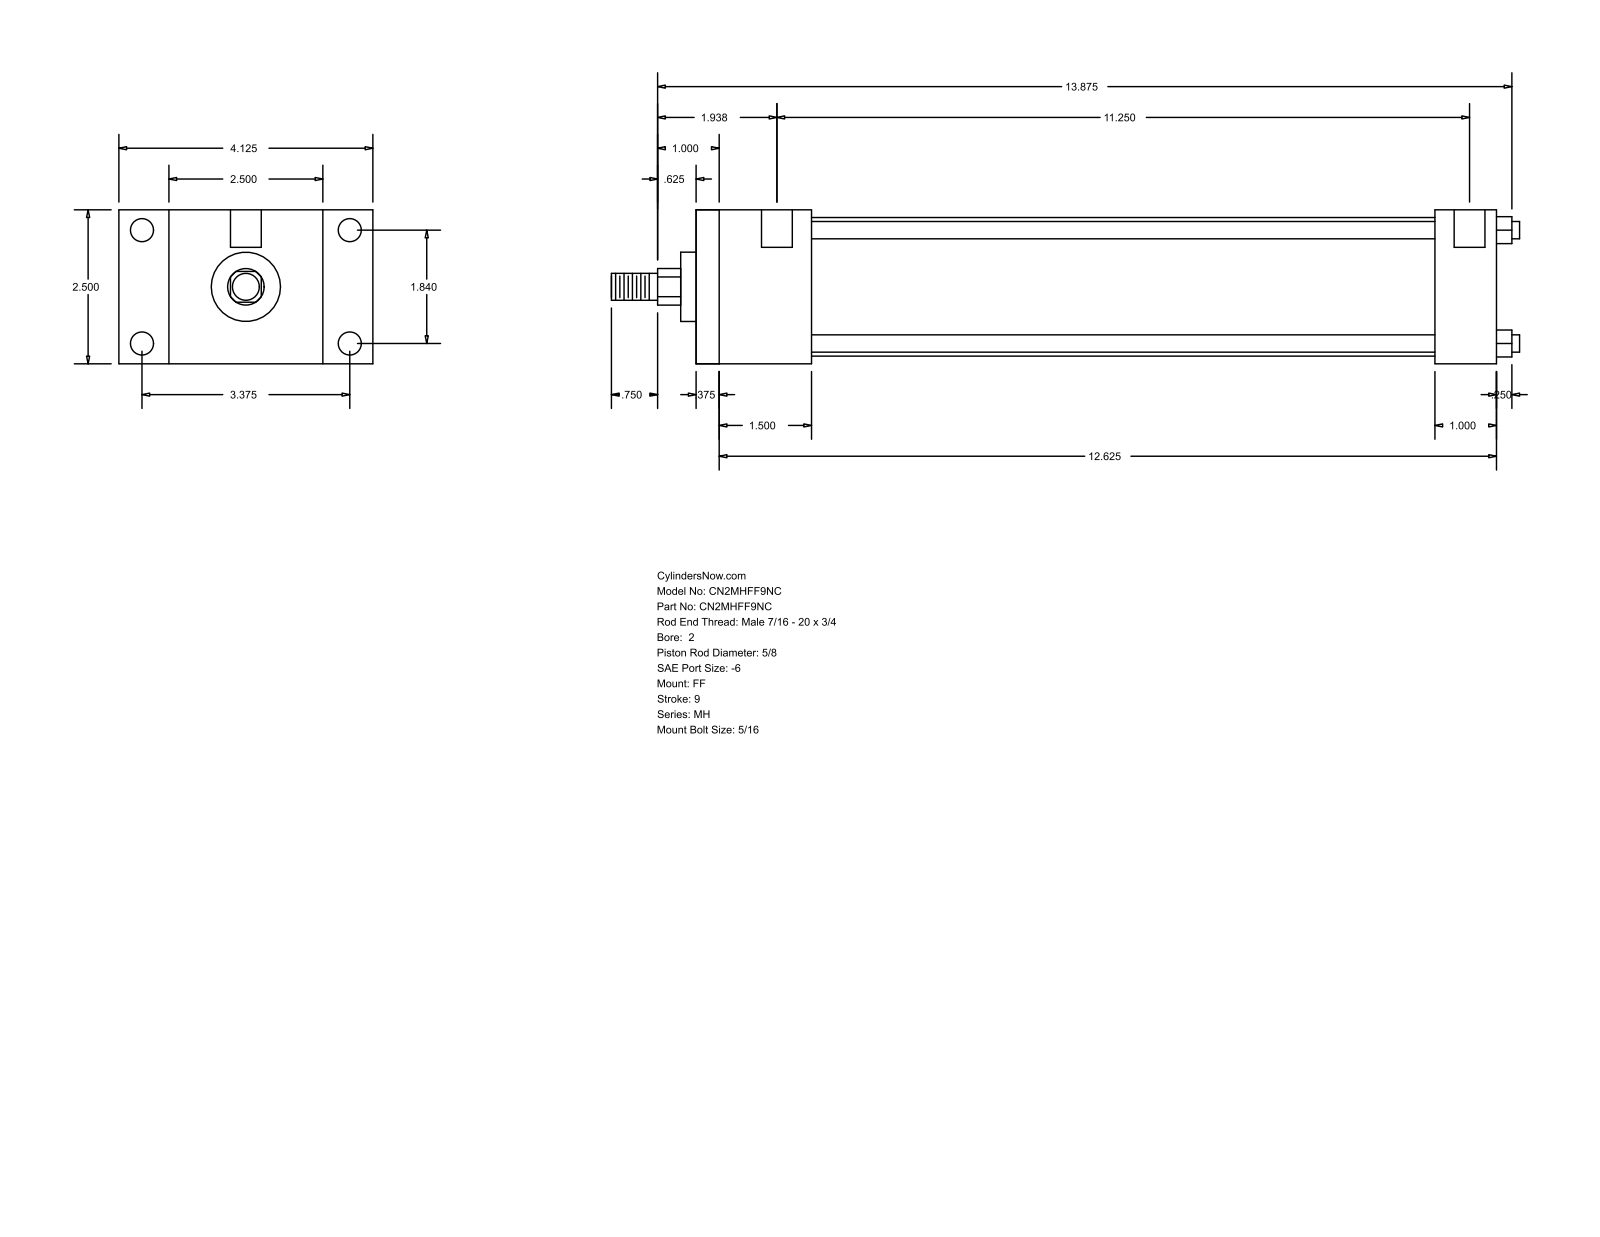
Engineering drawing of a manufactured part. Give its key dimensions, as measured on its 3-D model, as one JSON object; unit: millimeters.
{"part_name": "MH_FF__0200_0.625", "step_written_by": "GSSL Pune (CONFIG_CONTROL_DESIGN)", "units": "millimeters", "bodies": {"solids": 0, "faces": 92, "planar": 64, "cylindrical": 28, "other": 0}, "overall_size": [374.65, 104.78, 63.5], "round_holes": [[5.56, 4], [9.53, 4], [12.7, 2]], "round_bosses_or_shafts": [[7.14, 4], [57.15, 1], [28.57, 1], [15.88, 1], [11.11, 1]], "partial_cylinders_radius": [[7.54, 1]], "face_to_face_distances": [63.5, 330.19, 9.52, 320.67, 38.1, 47.62, 304.8, 295.28, 257.18, 282.57], "hole_center_spacings": [46.74, 85.72, 97.63, 293.69, 3.18, 4.76, 285.75, 288.93]}
